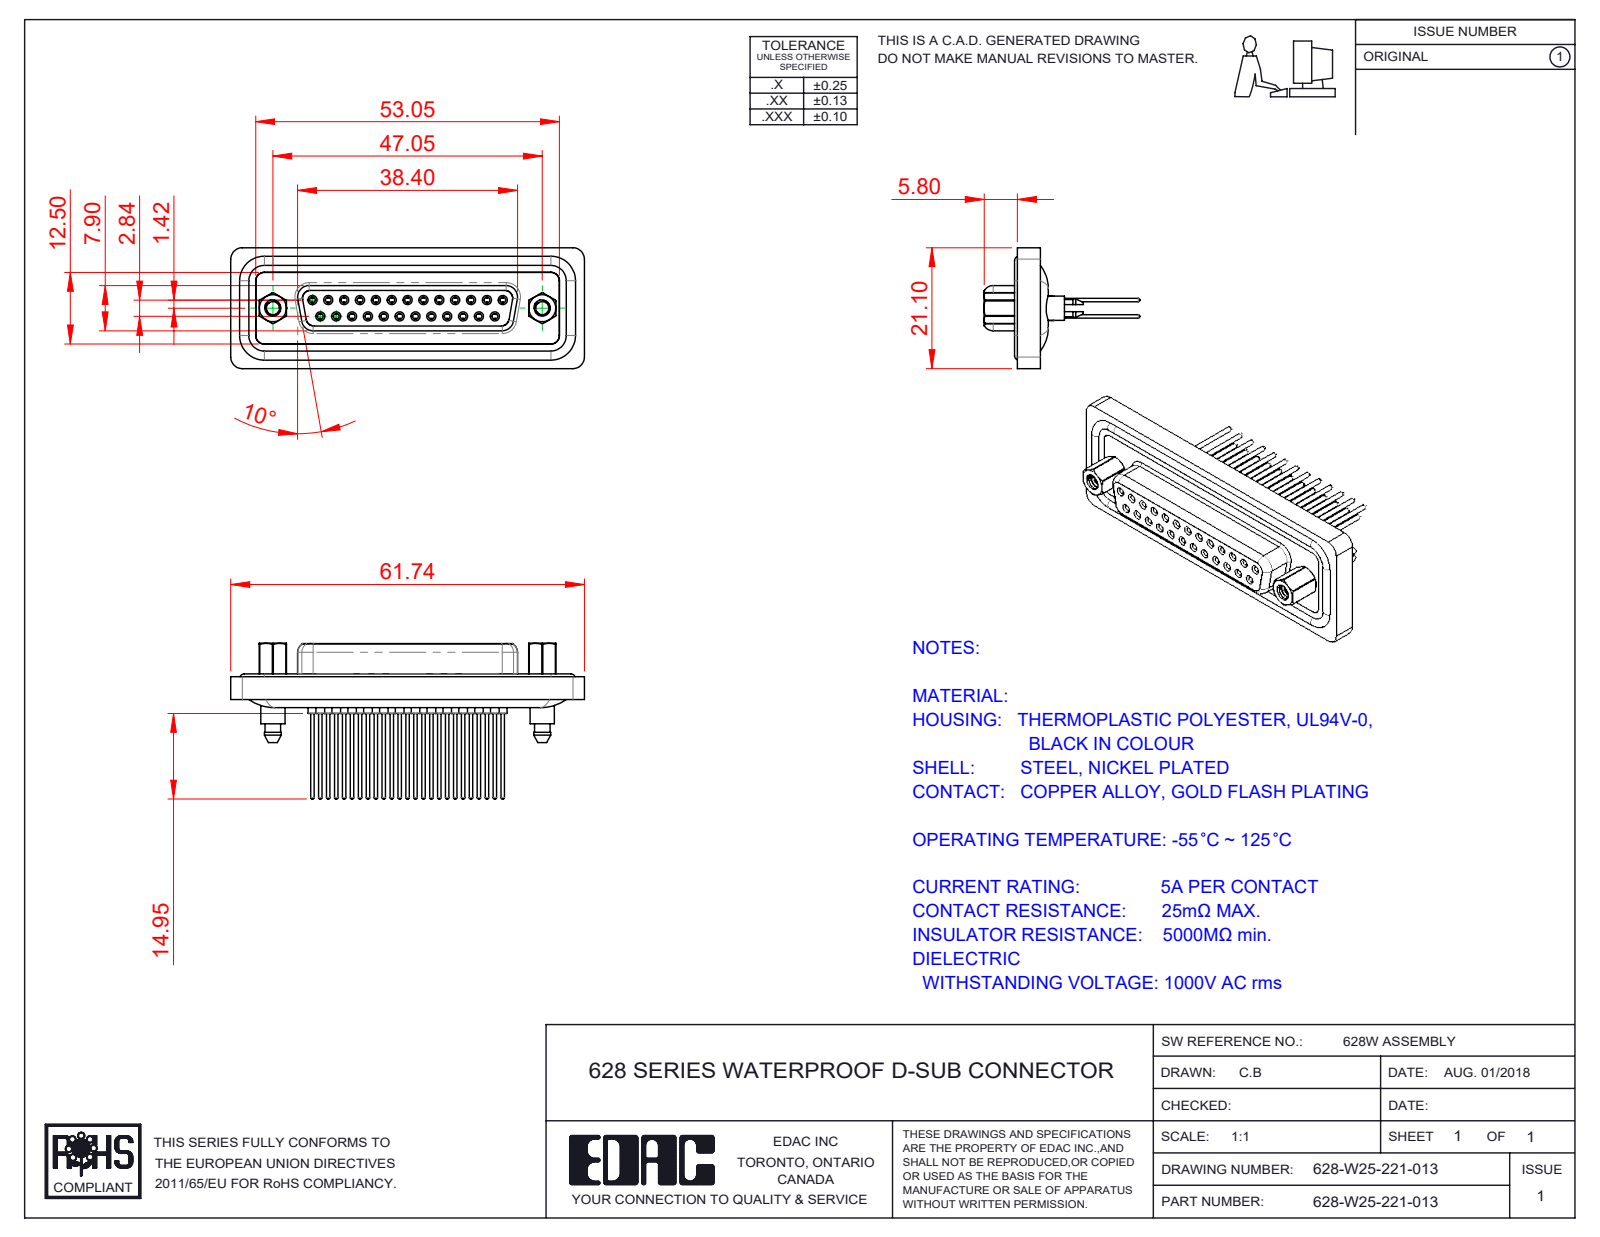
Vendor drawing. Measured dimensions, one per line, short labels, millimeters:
name: 628W Contact Row 1_21; 628W 4-40 Threaded Boardlock; 628W Housing_25 Contacts; 628-W25-221-013 (+4 more)
written by: SolidWorks 2020 (CONFIG_CONTROL_DESIGN)
unit: mm
bodies: 33 solids, 1894 faces (490 planar, 773 cylindrical, 631 other)
size: 61.74 × 27.2 × 21.1
volume: 7 521 mm³; area: 13 700 mm²
holes: 25× ⌀1, 25× ⌀1.1, 25× ⌀1.5, 25× ⌀1.7, 25× ⌀1.8, 25× ⌀2, 2× ⌀2.26, 2× ⌀2.29, 2× ⌀4, 2× ⌀4.25, 2× ⌀4.8
bosses: 29× ⌀1.6, 25× ⌀2.2, 25× ⌀0.6, 12× ⌀1.5, 2× ⌀5.4, 2× ⌀4.9, 2× ⌀2.79, 1× ⌀4.8
rounds: 16× R1.5, 14× R2, 8× R1.35, 6× R1.6, 4× R0.5, 4× R0.9, 4× R1.75, 4× R2.7
face distances: 0.4, 1.8, 1.6, 2.9, 2.5, 1.1, 7.45, 13.65, 4.1, 6.2
hole spacings: 3.16, 2.77, 5.54, 8.31, 11.08, 13.85, 5.03, 5.04
